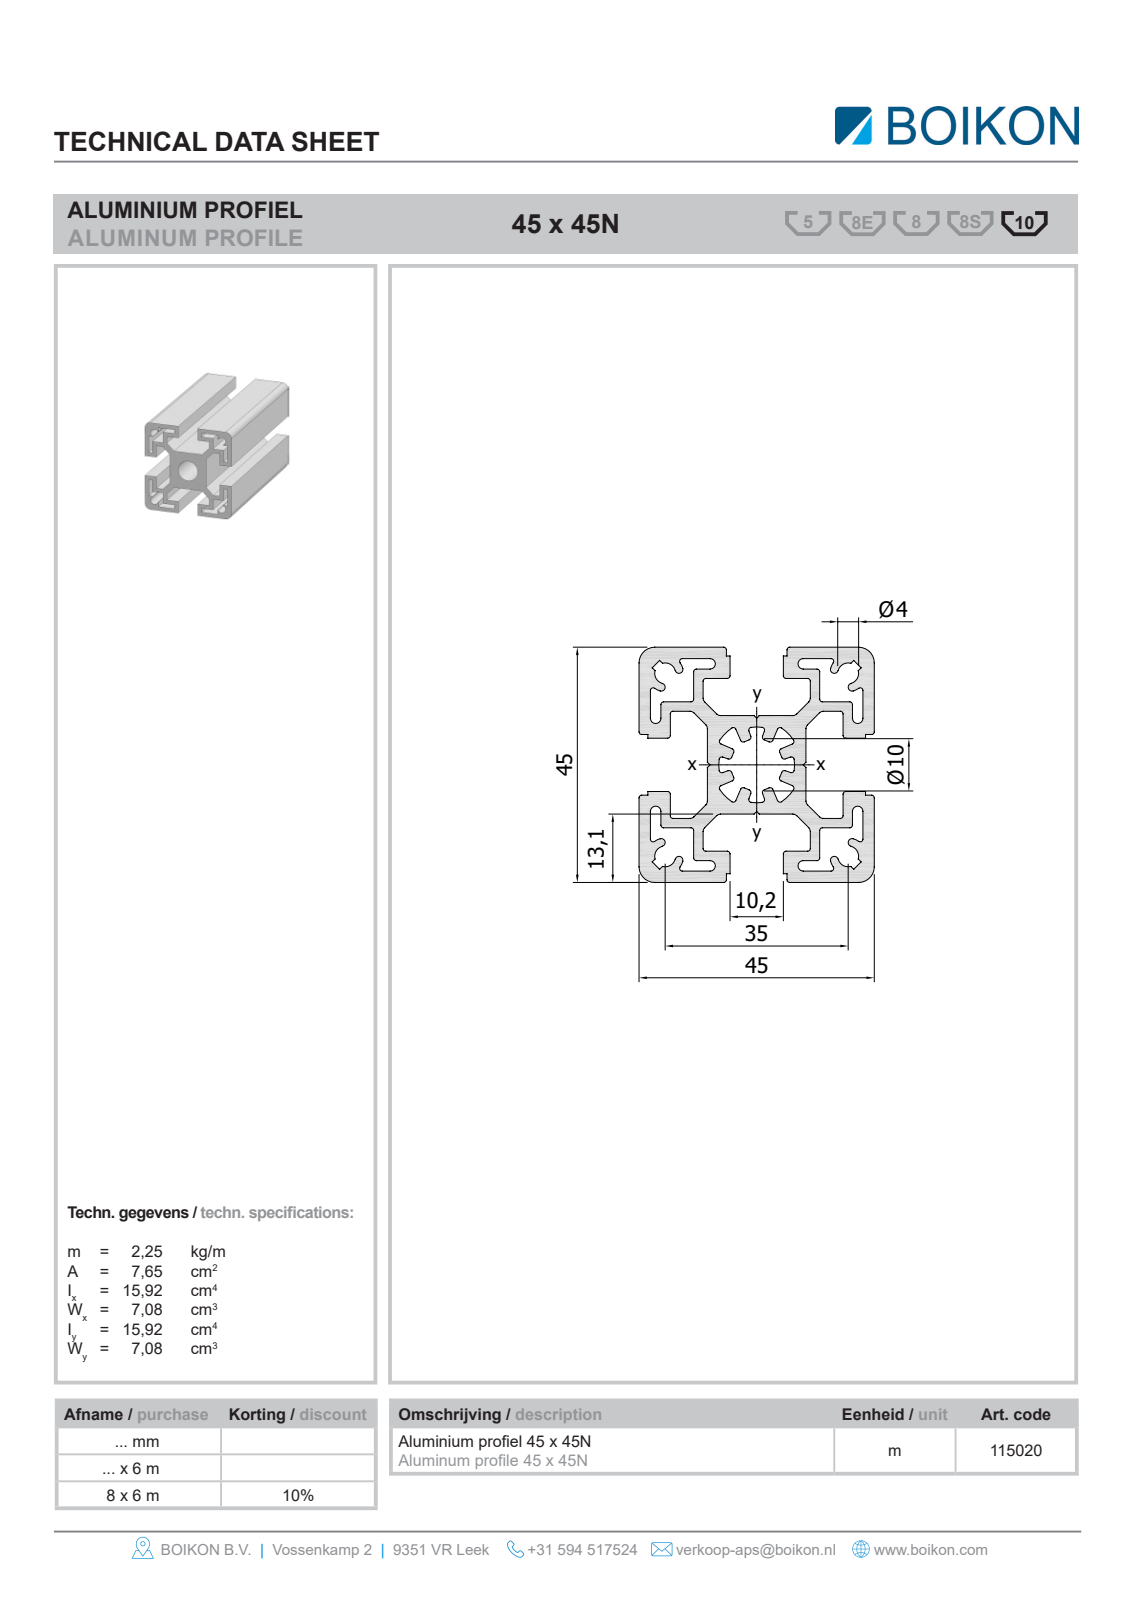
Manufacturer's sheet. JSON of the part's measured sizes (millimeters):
{"part_name": "Root; 11502045x45NBOIKON0", "step_written_by": "HiCAD 2013 1802.4 Build 509 (AUTOMOTIVE_DESIGN)", "units": "millimeters", "bodies": {"solids": 1, "faces": 103, "planar": 86, "cylindrical": 17, "other": 0}, "overall_size": [1000, 45, 45], "volume_mm3": 847890, "surface_area_mm2": 614416, "round_holes": [[10.2, 1]], "partial_cylinders_radius": [[0.1, 8], [2, 4], [3, 4]], "face_to_face_distances": [2, 4, 39, 41, 9.5, 33.5, 7.5, 31.5, 5.5, 29.5]}
